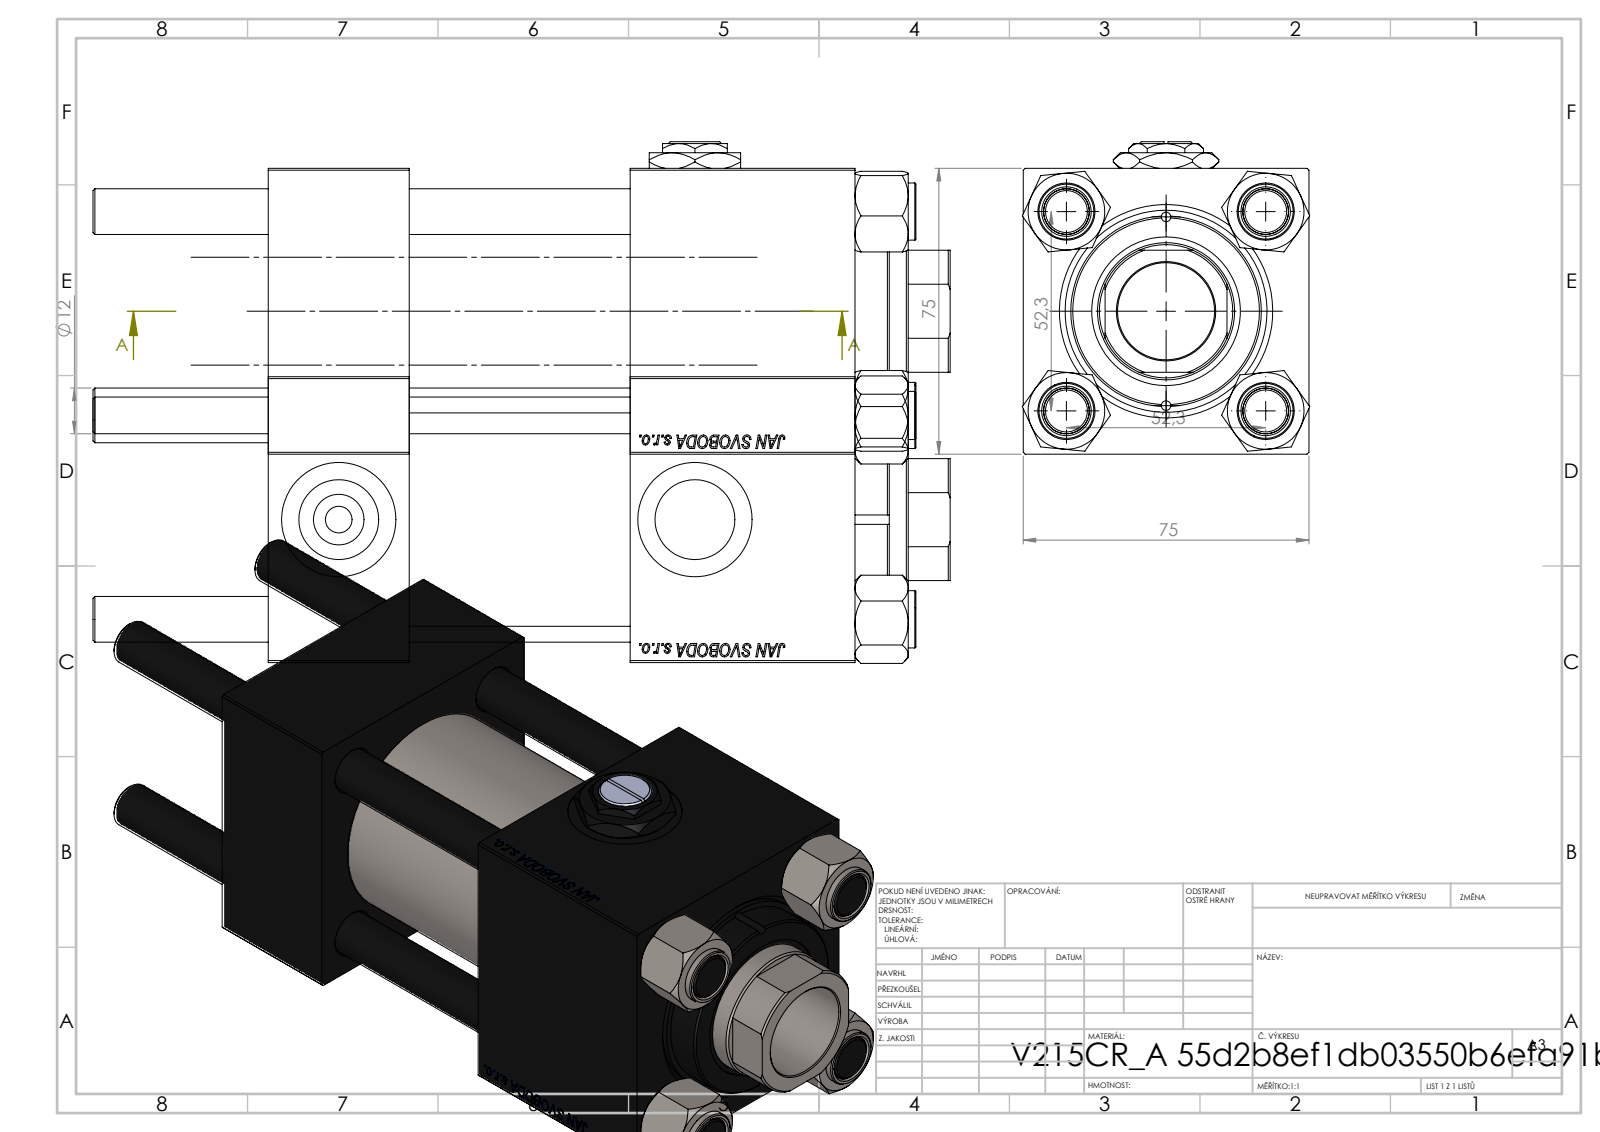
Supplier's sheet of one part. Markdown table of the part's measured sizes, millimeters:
| quantity | value |
| --- | --- |
| part name | V215_VC_A; V215CR_VCP; NUT_M5; V215CR_BODY_A (+2 more) |
| STEP written by | SolidWorks 2019 (CONFIG_CONTROL_DESIGN) |
| units | millimeters |
| bodies | 12 solids, 1187 faces (545 planar, 86 cylindrical, 556 other) |
| overall size | 225 × 82 × 75.43 |
| volume | 715 624 mm³ |
| surface area | 174 040 mm² |
| round holes (diameter × count) | 12 × 4, 2.5 × 2, 7 × 2, 20.96 × 2, 30 × 2, 25.5 × 1, 36 × 1, 39 × 1, 41 × 1, 53 × 1 |
| round bosses / shafts (diameter × count) | 15 × 4, 56 × 1, 50 × 1 |
| partial cylindrical surfaces (radius × count) | 17.5 × 1 |
| main face-to-face distances | 75, 37, 95, 154, 117, 59, 58, 125.3, 88.3, 30.3 |
| hole center spacings | 26.19, 36.98, 52.3, 57.22, 24.75, 73.96, 49.5, 93.5 |
